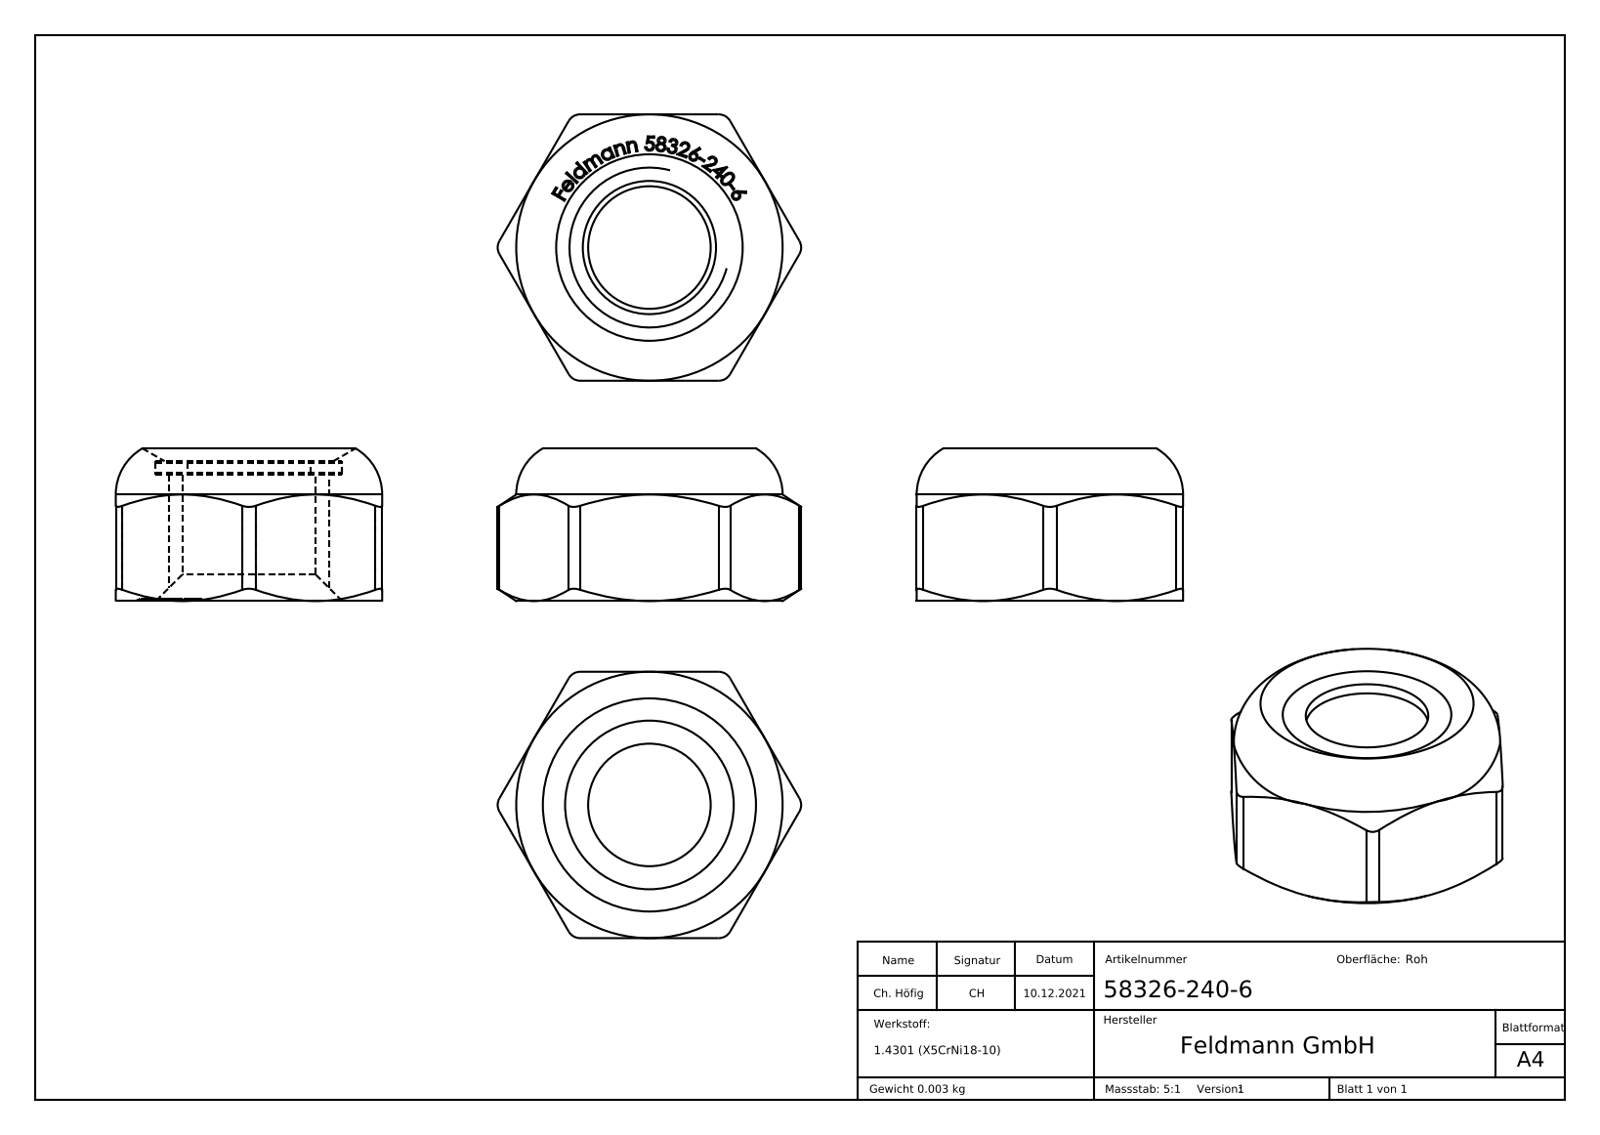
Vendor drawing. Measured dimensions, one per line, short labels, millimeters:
name: 58326-240-6
written by: SolidWorks 2018 (CONFIG_CONTROL_DESIGN)
unit: mm
bodies: 2 solids, 292 faces (141 planar, 10 cylindrical, 141 other)
size: 11.39 × 10 × 5.73
volume: 332 mm³; area: 453 mm²
holes: 1× ⌀4.6, 1× ⌀5, 1× ⌀7
rounds: 6× R0.5
face distances: 10, 0.45, 0.4, 4.8, 5.2, 4.75, 5.25, 0.5, 4.65, 4.7
